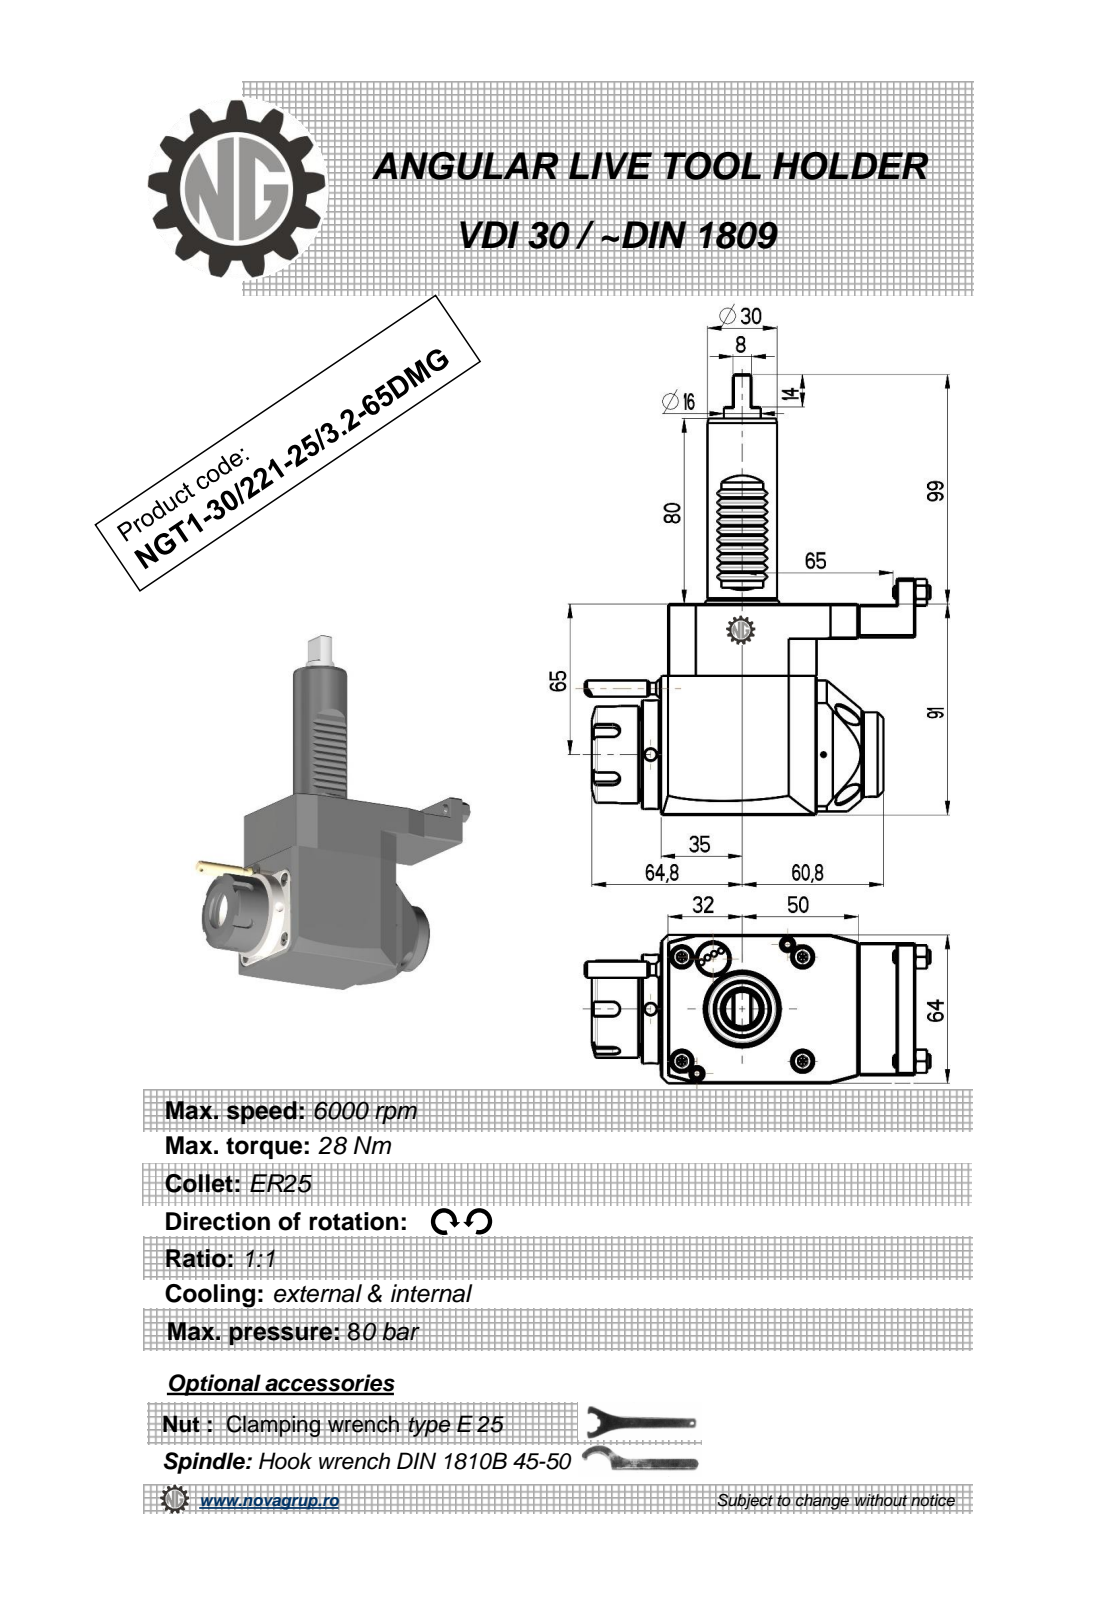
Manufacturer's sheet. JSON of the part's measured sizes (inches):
{"part_name": "NGT1_30_225_25_3_2_65DMG", "step_written_by": "PRO/ENGINEER BY PARAMETRIC TECHNOLOGY CORPORATION, 2010280 (CONFIG_CONTROL_DESIGN)", "units": "inches", "bodies": {"solids": 1, "faces": 419, "planar": 181, "cylindrical": 76, "other": 162}, "overall_size": [7.48, 5.859, 2.52], "volume_in3": 34.59, "surface_area_in2": 92.44, "round_holes": [[0.197, 2], [0.098, 1], [0.118, 1], [0.799, 1]], "round_bosses_or_shafts": [[0.236, 2], [1.85, 1], [1.654, 1], [1.496, 1], [1.437, 1], [1.378, 1], [1.299, 1], [1.181, 1]], "partial_cylinders_radius": [[0.012, 10], [0.012, 10], [0.118, 5], [0.031, 2], [1.26, 1]], "face_to_face_distances": [2.52, 3.583, 0.02, 0.571, 4.319, 0.315, 3.012, 1.673, 0.126, 2.646], "hole_center_spacings": [1.307]}
